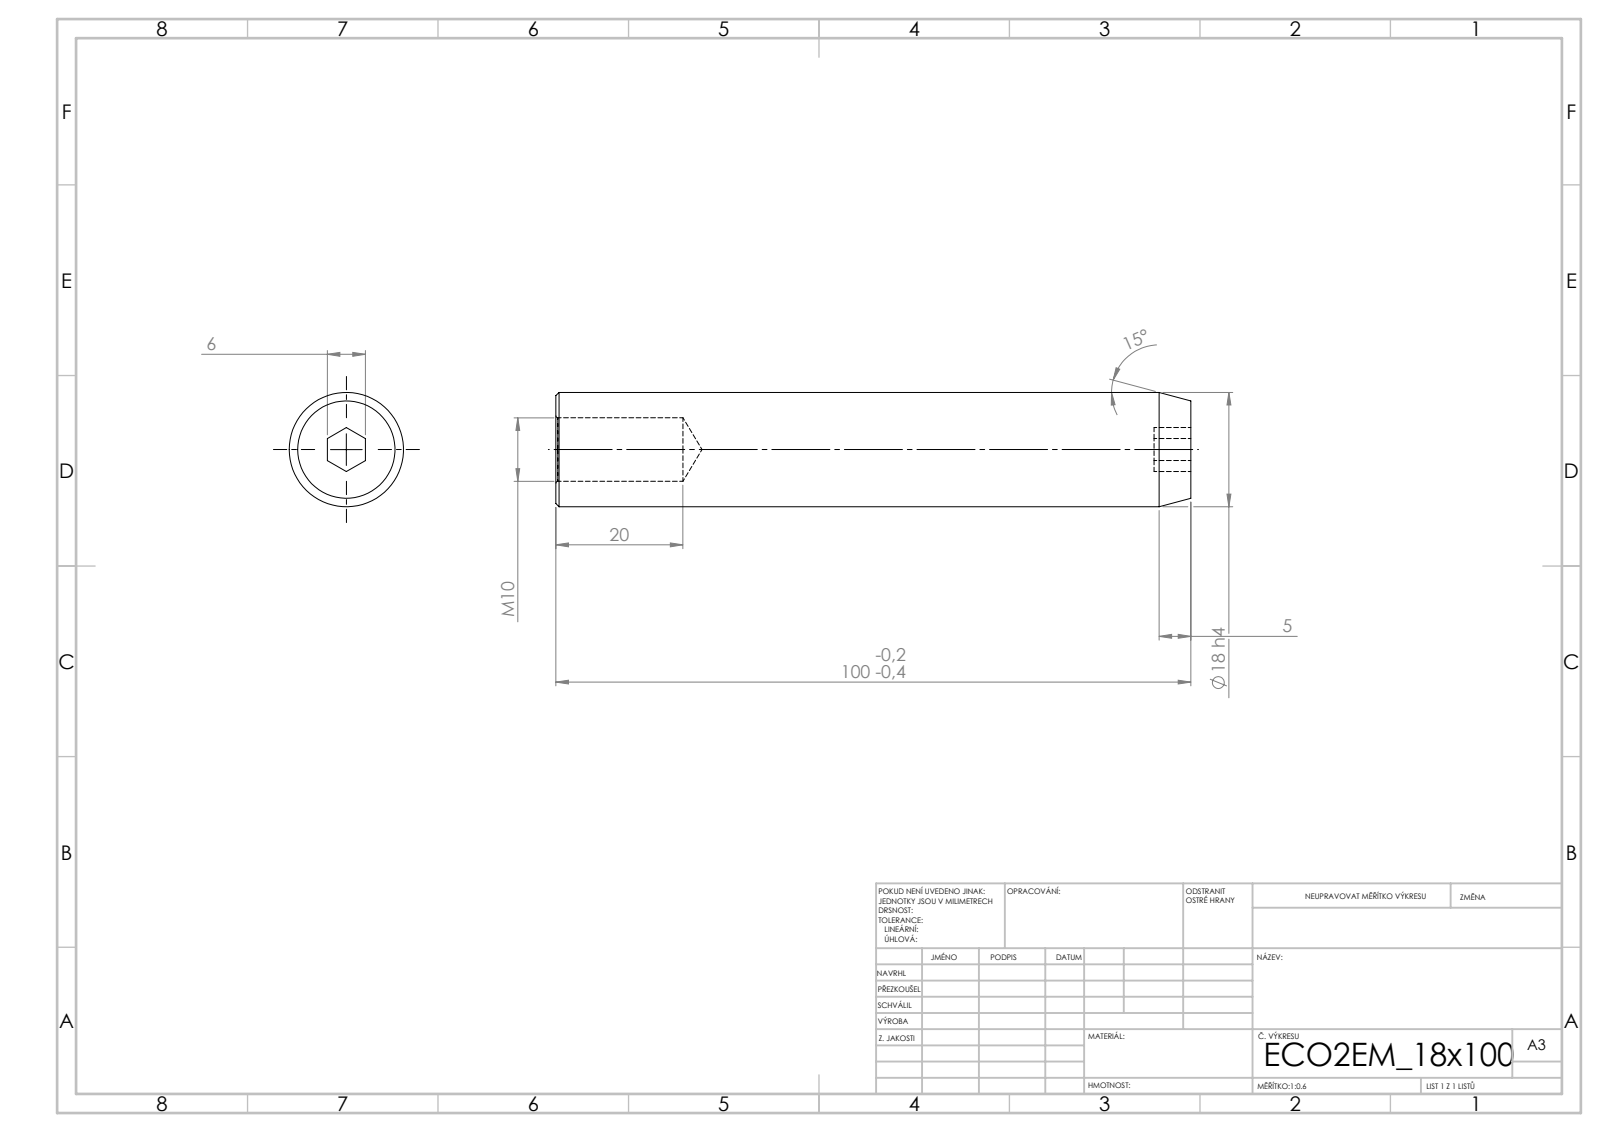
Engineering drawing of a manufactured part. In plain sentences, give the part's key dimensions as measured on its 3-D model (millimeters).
Its 3-D file was written by "SolidWorks 2019 (CONFIG_CONTROL_DESIGN)". It is 1 solid with 21 faces: 9 planar, 4 cylindrical and 8 other. Overall it measures 100 by 18 by 18 millimeters. Its volume is 23 429 cubic millimeters and its surface area 6 823 square millimeters. Round holes: 1 of diameter 10. Round bosses or shafts: 1 of diameter 18. The main face-to-face distances are 100, 6, 5.8, 94.2.
